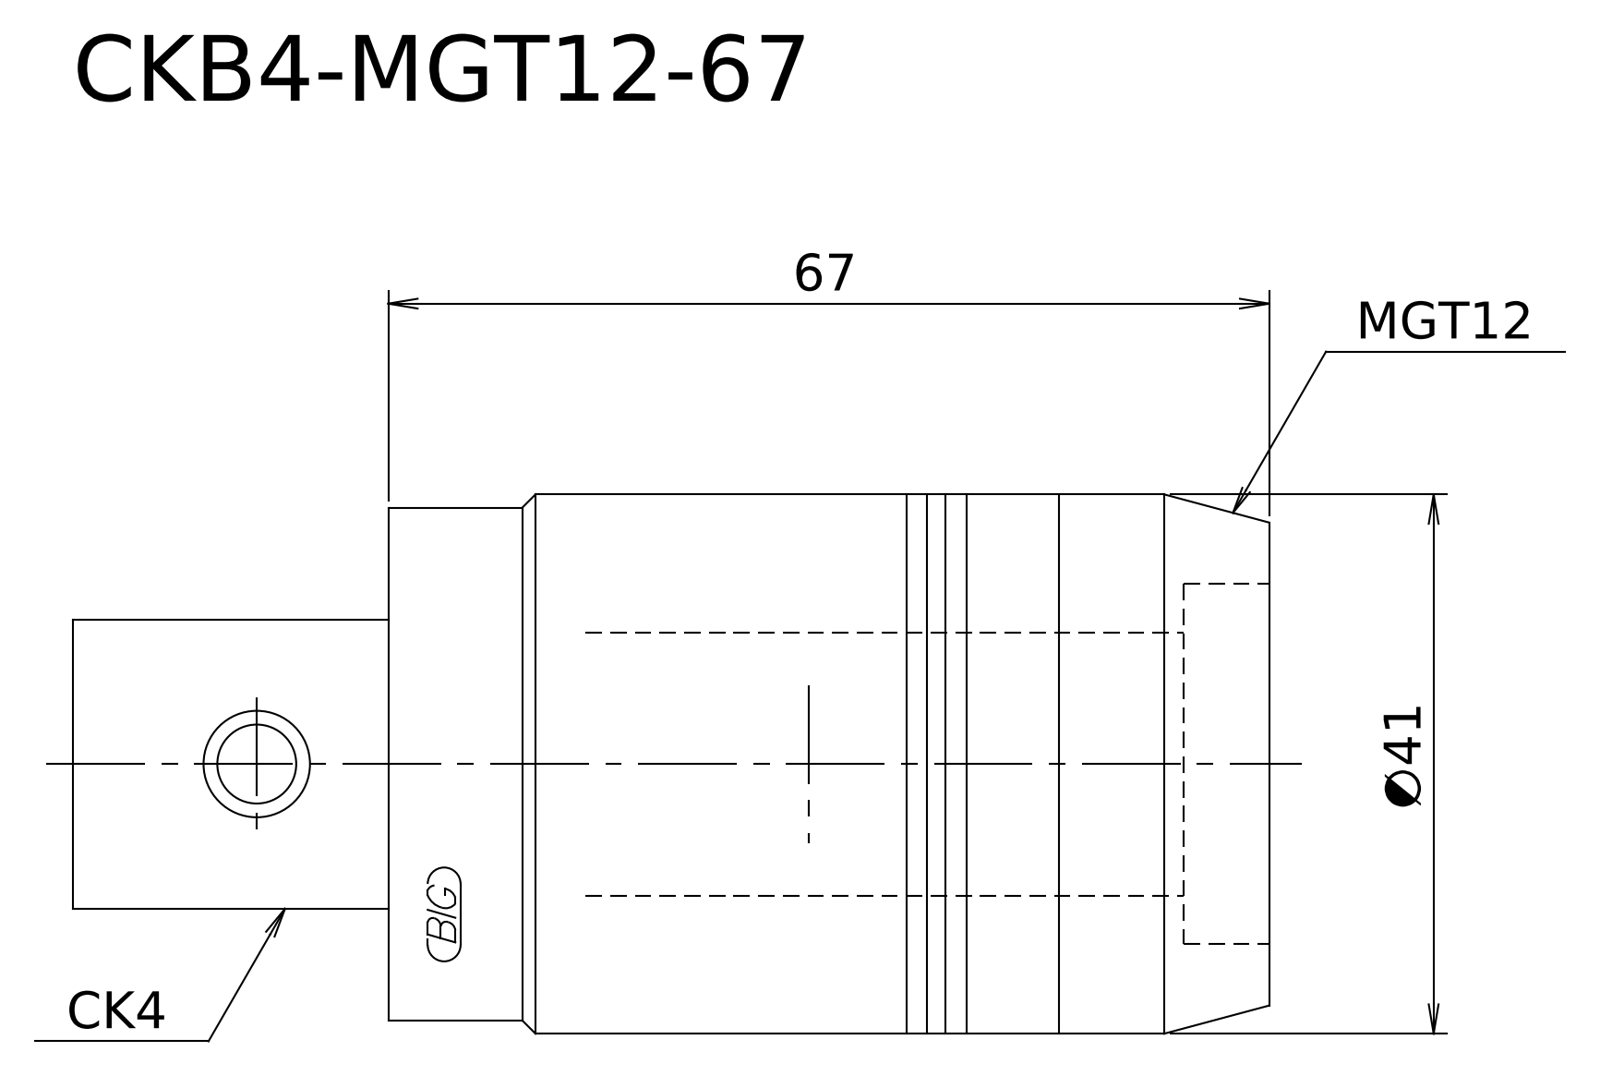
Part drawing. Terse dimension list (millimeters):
written by: Kubotek KeyCreator V8.5.1 (14335) (CONFIG_CONTROL_DESIGN)
unit: mm
bodies: 1 solid, 14 faces (2 planar, 6 cylindrical, 6 other)
size: 67 × 41 × 41
volume: 85 923 mm³; area: 10 927 mm²
bosses: 1× ⌀41, 1× ⌀40.2, 1× ⌀39
face distances: 67
